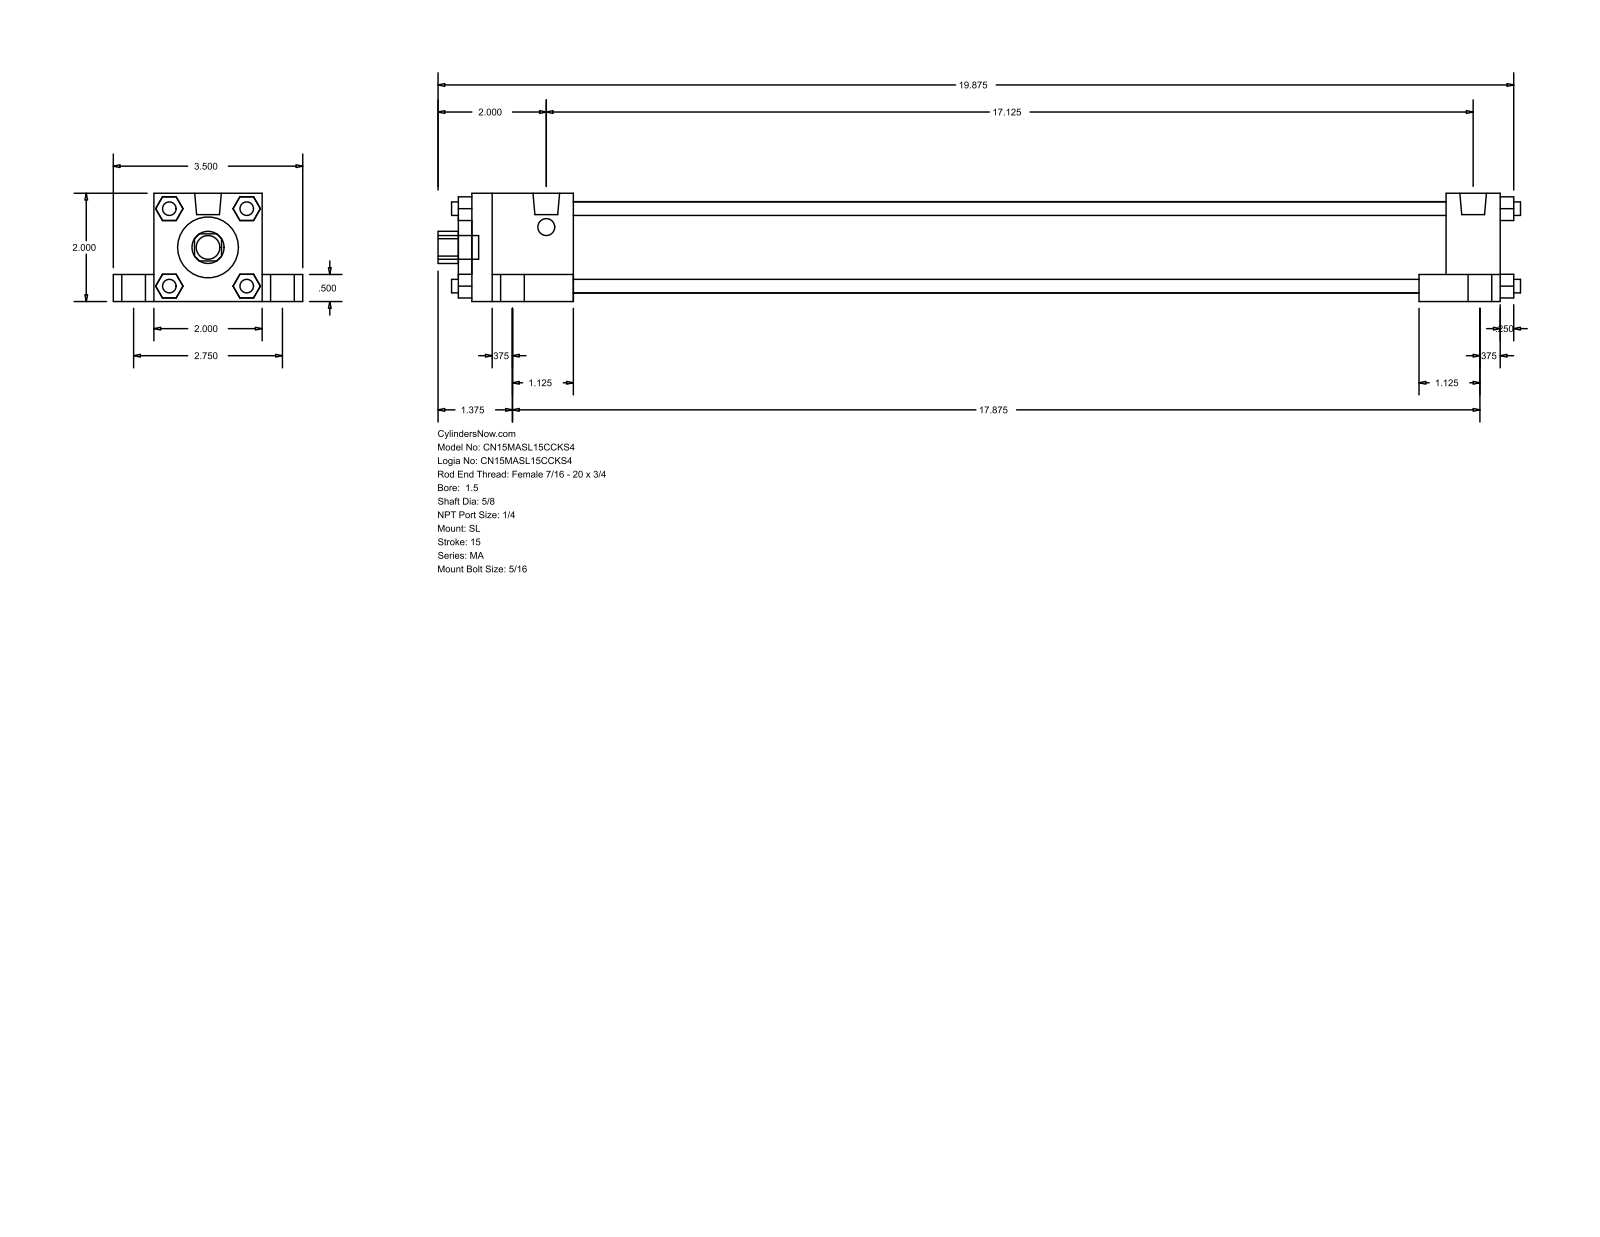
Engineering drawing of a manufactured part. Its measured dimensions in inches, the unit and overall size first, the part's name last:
Units: inches
Overall size (bounding box): 20 × 3.5 × 2
Round holes (diameter × count): ⌀0.625 ×1, ⌀1.125 ×1, ⌀1.69 ×1
Round bosses / shafts (diameter × count): ⌀0.437 ×5, ⌀0.687 ×4, ⌀0.313 ×4, ⌀0.25 ×4, ⌀0.492 ×2
Partial cylindrical surfaces — rounded edges, fillets, slot ends (radius × count): R0.297 ×1
Main face-to-face distances: 2, 0.75, 1.5, 0.5, 19, 2.75, 16.125, 0.375, 18, 1
Bodies: 0 solids, 148 faces (112 planar, 36 cylindrical, 0 other)
Part name (STEP PRODUCT): MA_SL__0150_0.625
STEP written by: GSSL Pune (CONFIG_CONTROL_DESIGN)
